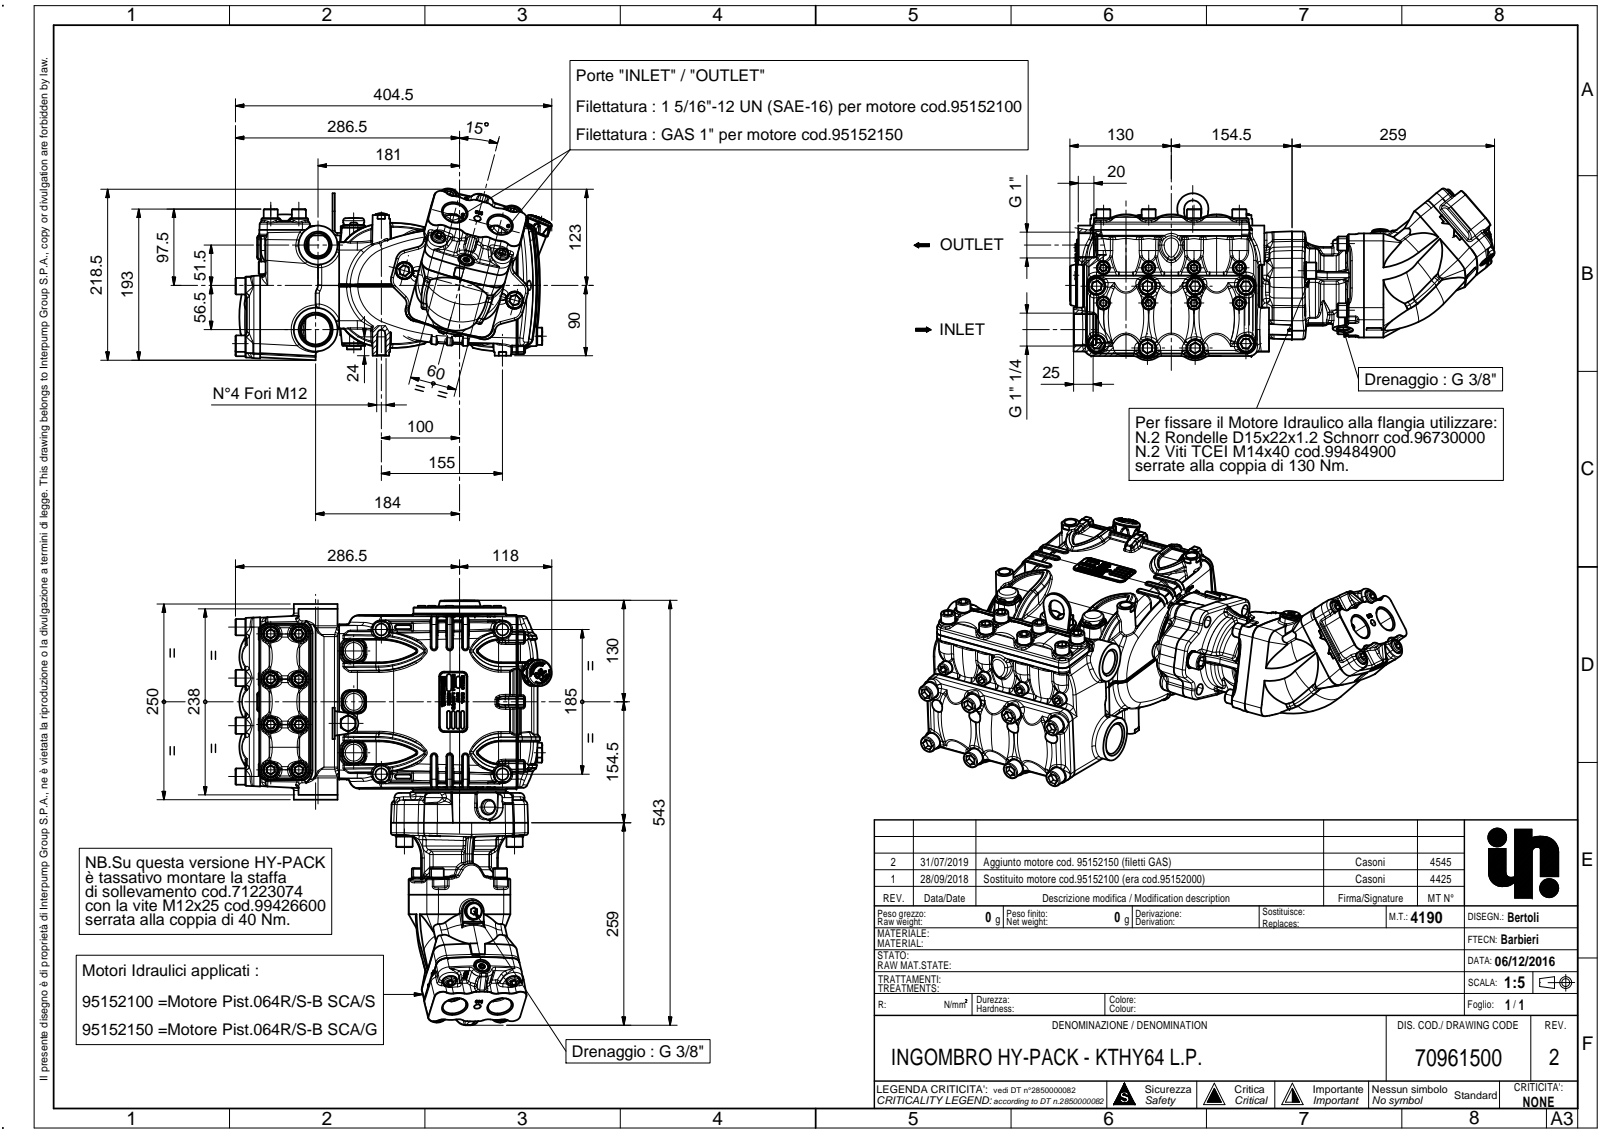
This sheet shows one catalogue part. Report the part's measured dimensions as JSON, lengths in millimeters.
{"step_written_by": "THINKDESIGN (CONFIG_CONTROL_DESIGN)", "units": "millimeters", "bodies": {"solids": 236, "faces": 19728, "planar": 4882, "cylindrical": 4991, "other": 9855}, "overall_size": [543.36, 404.65, 219.71], "volume_mm3": 14220000, "surface_area_mm2": 1529000, "round_holes": [[9, 25], [6.5, 20], [12.5, 18], [10.5, 16], [8.5, 10], [10.25, 10], [5, 8], [11.8, 8], [12, 8], [12.25, 8], [14.25, 8], [14.5, 8]], "round_bosses_or_shafts": [[10, 26], [18, 19], [6, 14], [12, 13], [16, 12], [21, 9], [14, 9], [27, 5]], "partial_cylinders_radius": [[0.5, 1089], [0.1, 616], [1, 298], [3, 291], [1.5, 166], [2, 148], [0.2, 106], [5, 62]], "face_to_face_distances": [227, 101, 328, 7, 220, 321, 42.5, 224, 266.5, 7.9], "hole_center_spacings": [50, 38.27, 60.88, 79.34, 92.39, 99.15, 13.05, 25.88]}
